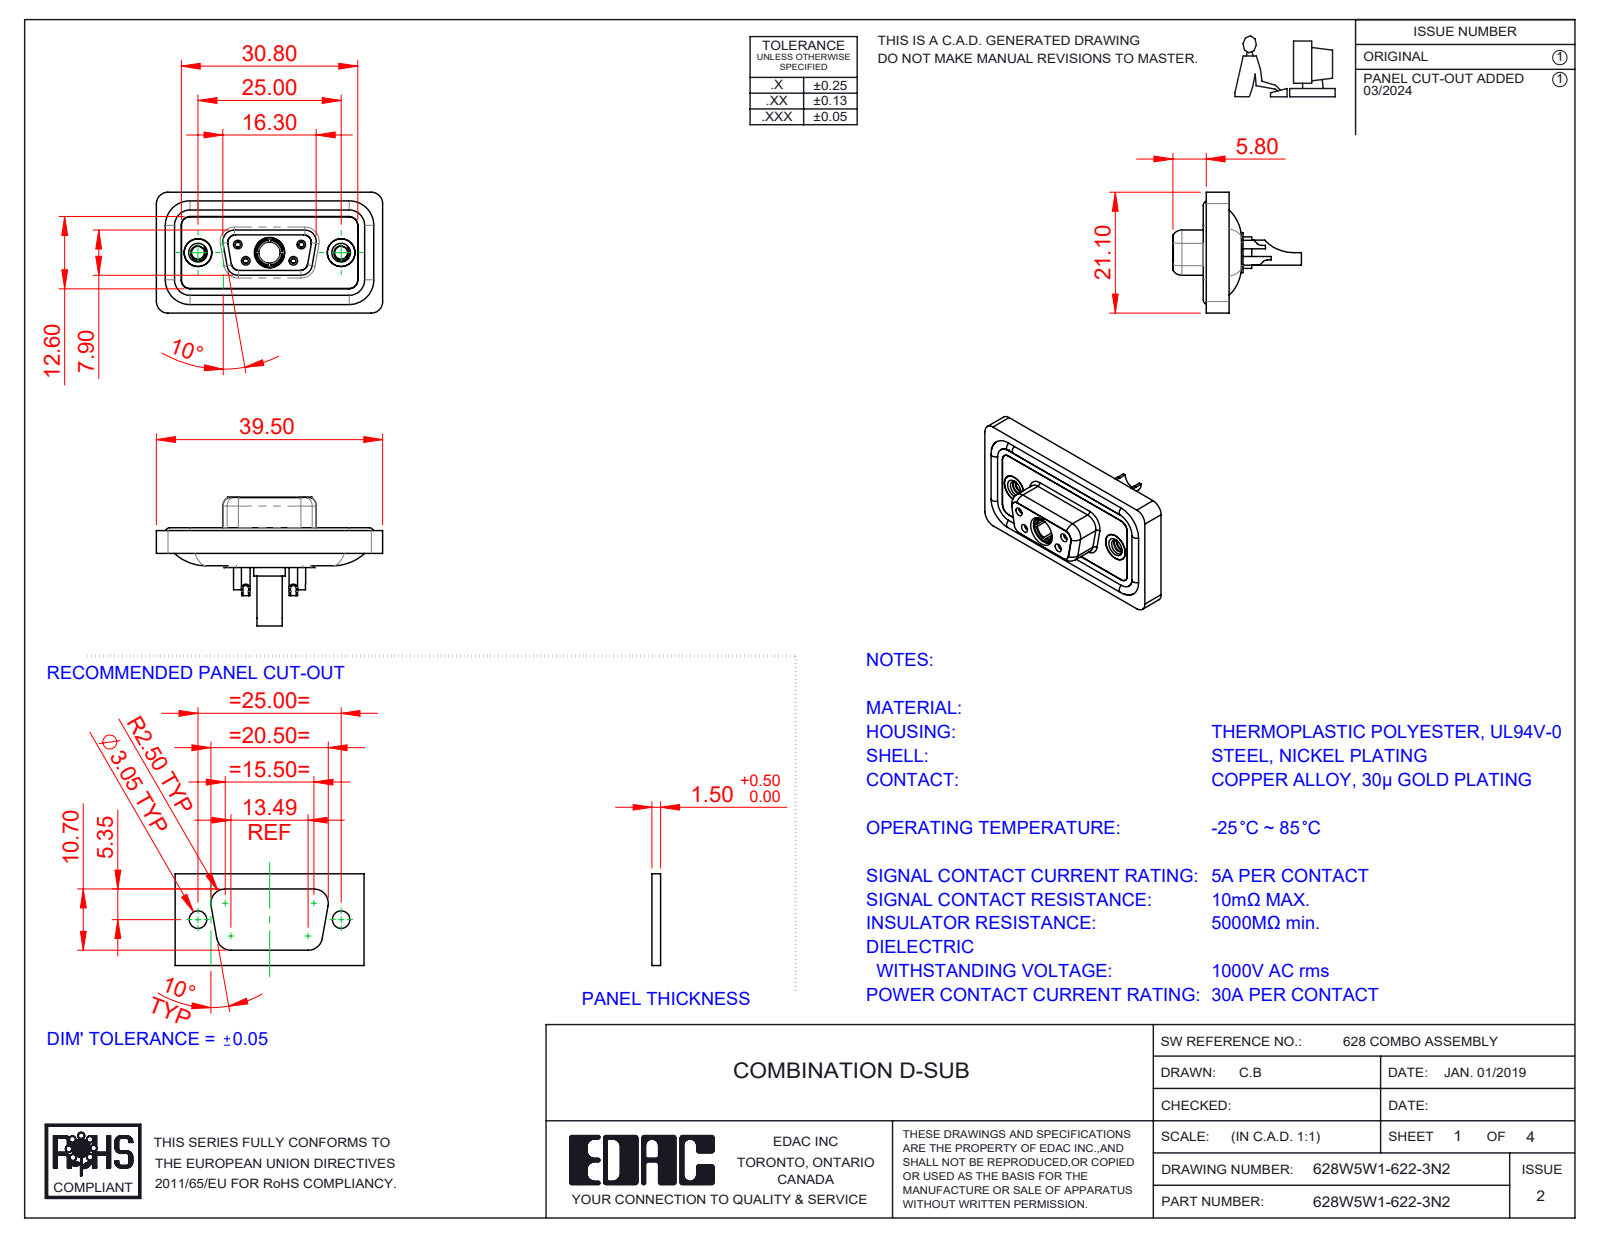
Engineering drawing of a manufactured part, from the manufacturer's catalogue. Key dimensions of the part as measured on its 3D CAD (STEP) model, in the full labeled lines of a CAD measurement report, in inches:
Part name (STEP PRODUCT): 628Combo Threaded Rivet_2; 628Combo Contact Row 2_22; 628Combo Contact Row 1_22; 628W5W1-622-3N2 (+5 more)
STEP written by: SolidWorks 2023 (CONFIG_CONTROL_DESIGN)
Units: inches
Bodies: 13 solids, 686 faces (205 planar, 298 cylindrical, 183 other)
Overall size (bounding box): 1.555 × 0.884 × 0.831
Volume: 0.293 in³ · Surface area: 12.07 in²
Round holes (diameter × count): ⌀0.035 ×4, ⌀0.039 ×4, ⌀0.043 ×4, ⌀0.059 ×4, ⌀0.079 ×4, ⌀0.191 ×3, ⌀0.063 ×2, ⌀0.067 ×2, ⌀0.089 ×2, ⌀0.157 ×2, ⌀0.159 ×2, ⌀0.197 ×2
Round bosses / shafts (diameter × count): ⌀0.063 ×6, ⌀0.087 ×4, ⌀0.195 ×2, ⌀0.189 ×2, ⌀0.217 ×1, ⌀0.205 ×1, ⌀0.195 ×1, ⌀0.187 ×1
Partial cylindrical surfaces — rounded edges, fillets, slot ends (radius × count): R0.059 ×22, R0.079 ×18, R0.053 ×8, R0.063 ×8, R0.039 ×6, R0.01 ×4, R0.02 ×4, R0.024 ×4
Main face-to-face distances: 0.016, 0.114, 0.043, 0.071, 0.063, 0.02, 0.222, 0.293, 0.211, 0.142
Hole centre spacings: 0.124, 0.225, 0.28, 0.492, 0.713, 0.173, 0.173, 0.327
